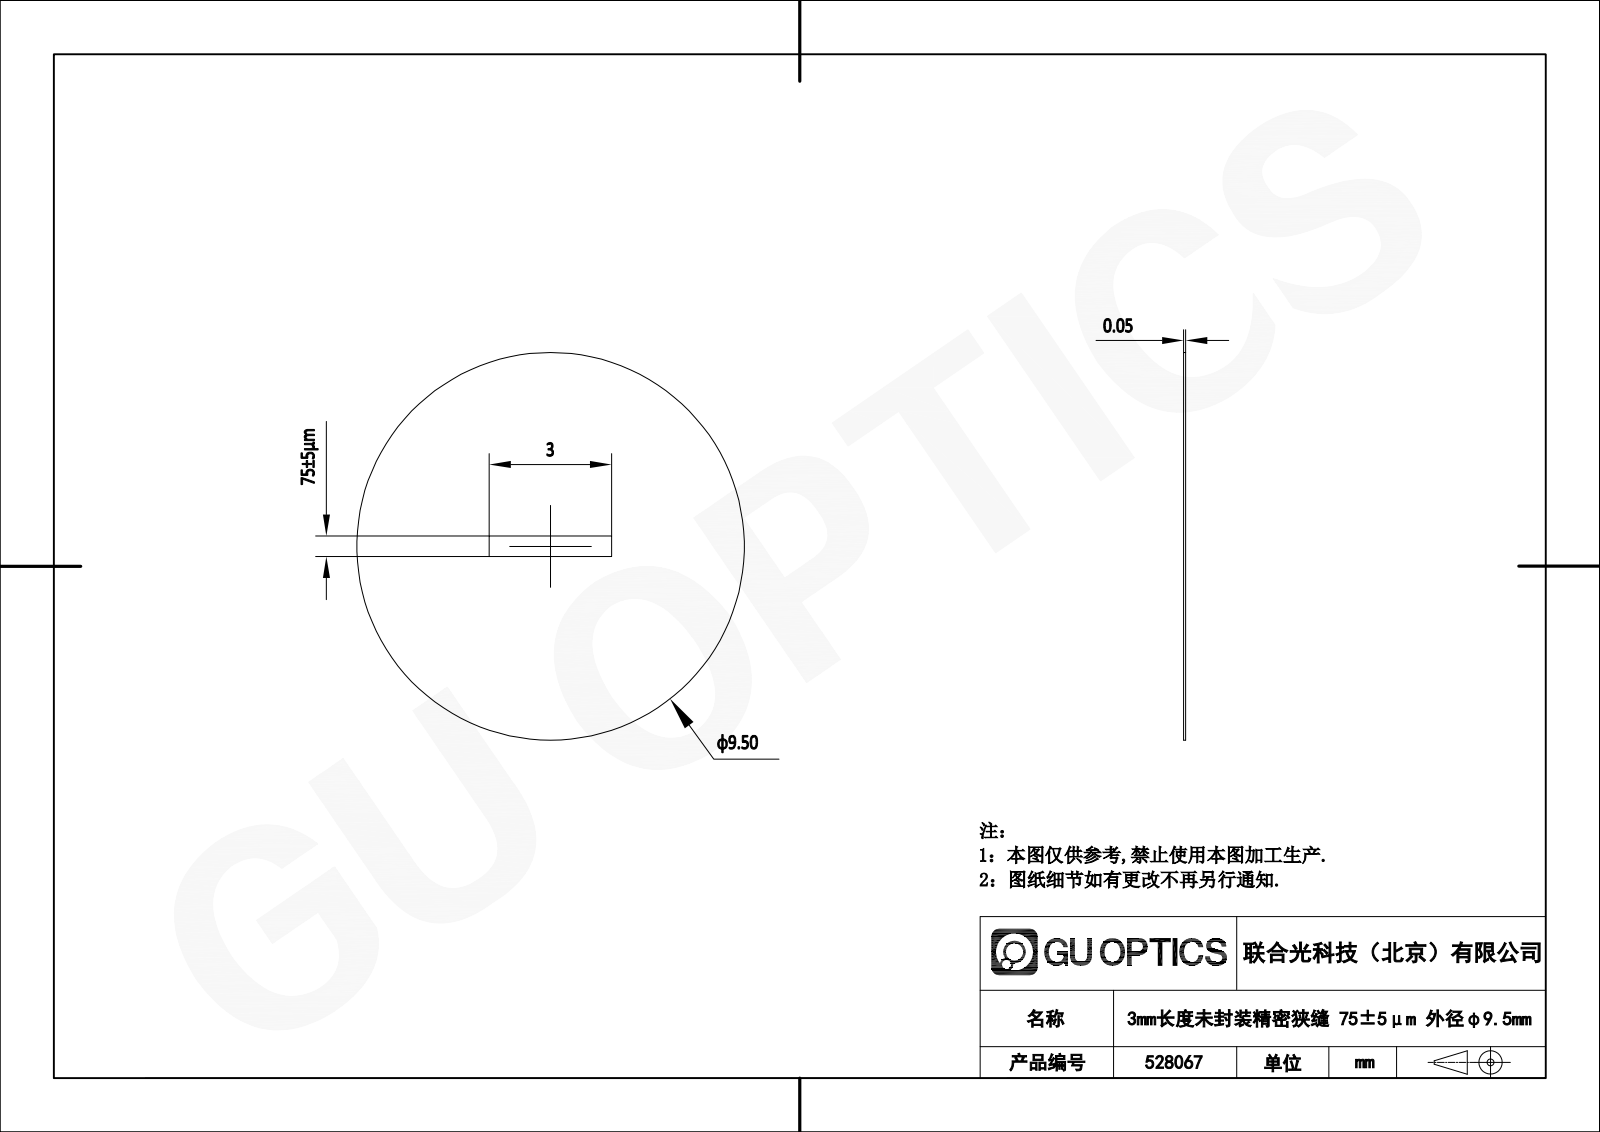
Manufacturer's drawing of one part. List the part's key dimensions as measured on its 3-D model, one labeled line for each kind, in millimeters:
Part name (STEP PRODUCT): 1.5.4.8-ZXG-9.5-75
STEP written by: SolidWorks 2021 (CONFIG_CONTROL_DESIGN)
Units: millimetres
Bodies: 1 solid, 8 faces (6 planar, 2 cylindrical, 0 other)
Overall size (bounding box): 9.5 × 9.5 × 0.05
Volume: 4 mm³ · Surface area: 143 mm²
Round bosses / shafts (diameter × count): ⌀9.5 ×1
Main face-to-face distances: 3
